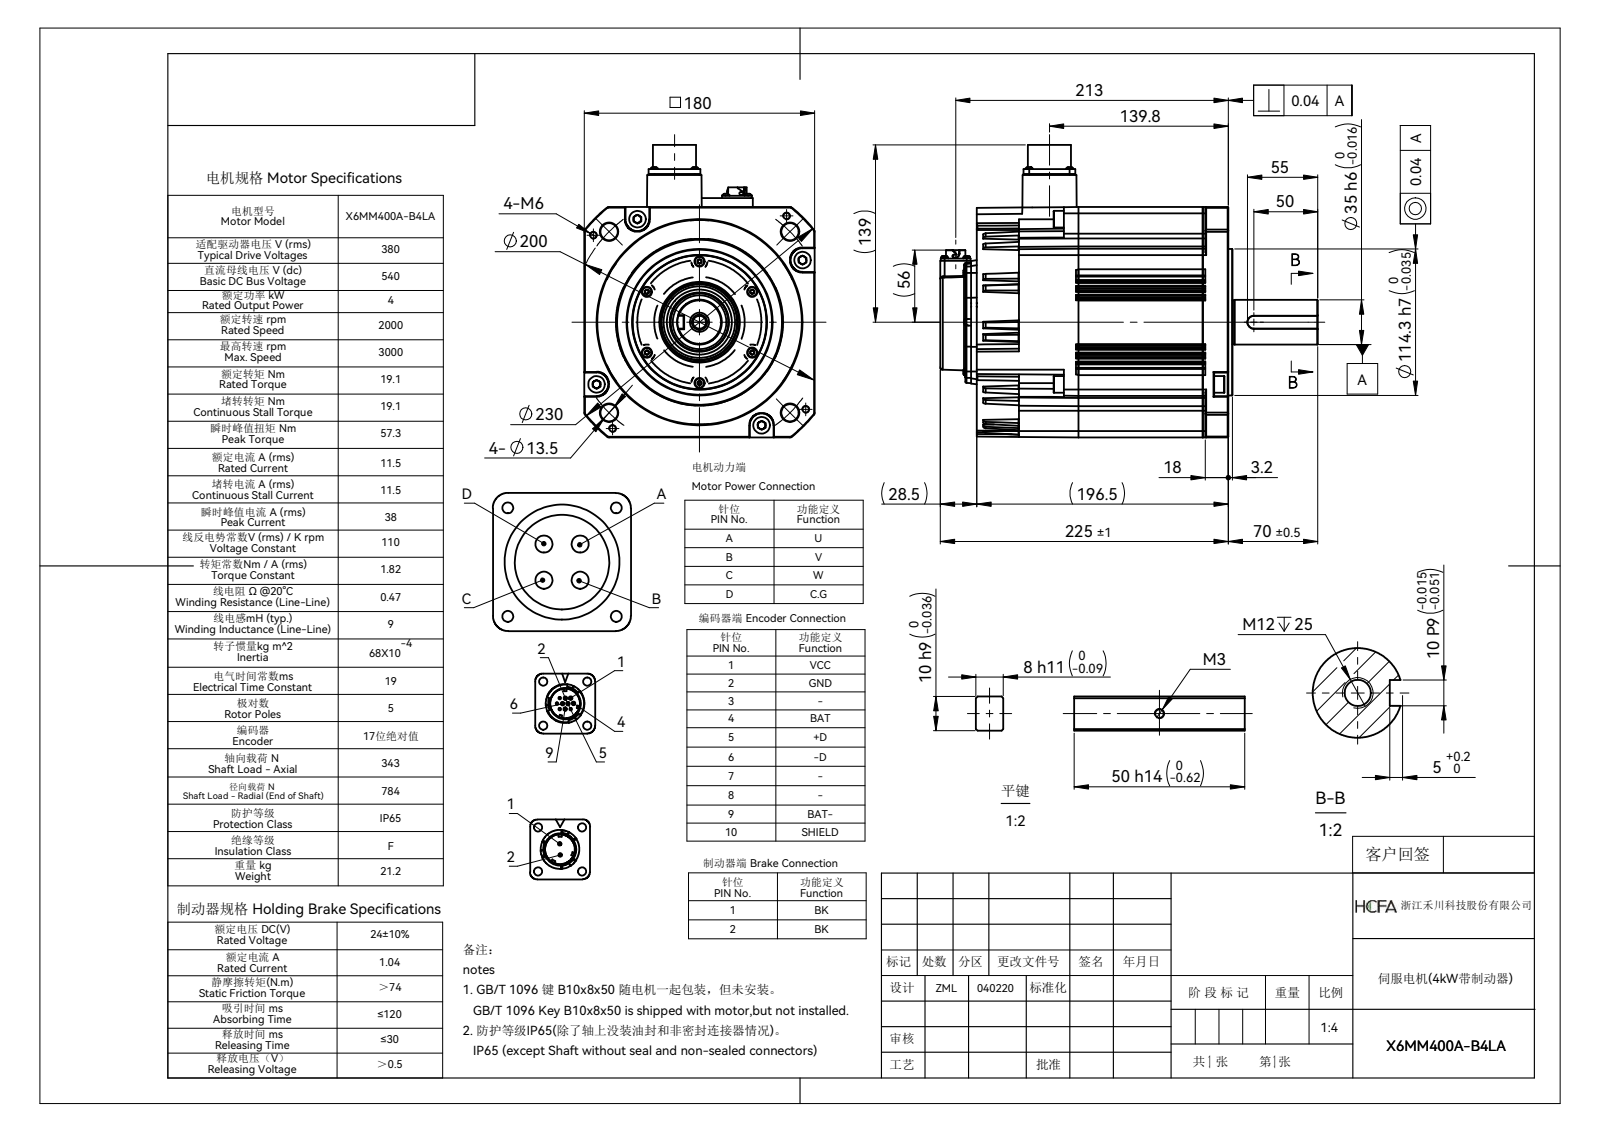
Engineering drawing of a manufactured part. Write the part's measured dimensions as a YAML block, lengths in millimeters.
part_name: "SV-X2MM400A-B4LA"
step_written_by: "SolidWorks 2016 (CONFIG_CONTROL_DESIGN)"
units: millimeters
bodies: {solids: 1, faces: 2030, planar: 773, cylindrical: 696, other: 561}
overall_size: [295, 228.55, 180]
volume: 5648000
surface_area: 265760
round_holes:
  - {diameter: 13.5, count: 4}
  - {diameter: 11.6, count: 2}
  - {diameter: 10.2, count: 1}
  - {diameter: 11.75, count: 1}
  - {diameter: 11.8, count: 1}
  - {diameter: 27.7, count: 1}
  - {diameter: 32.5, count: 1}
round_bosses_or_shafts:
  - {diameter: 5.7, count: 12}
  - {diameter: 1, count: 10}
  - {diameter: 13, count: 4}
  - {diameter: 5, count: 4}
  - {diameter: 15.2, count: 2}
  - {diameter: 0.75, count: 2}
  - {diameter: 114.3, count: 1}
  - {diameter: 35, count: 1}
partial_cylinders:
  - {radius: 0.5, count: 105}
  - {radius: 1, count: 48}
  - {radius: 5, count: 29}
  - {radius: 2, count: 18}
  - {radius: 0.55, count: 16}
  - {radius: 0.2, count: 8}
  - {radius: 3, count: 8}
  - {radius: 2.8, count: 4}
face_to_face_distances: [180, 32.5, 147.5, 196.5, 199.7, 3.2, 115, 4, 192.5, 7.2]
hole_center_spacings: [100, 141.42, 200, 48.75, 75.81, 78.87]
